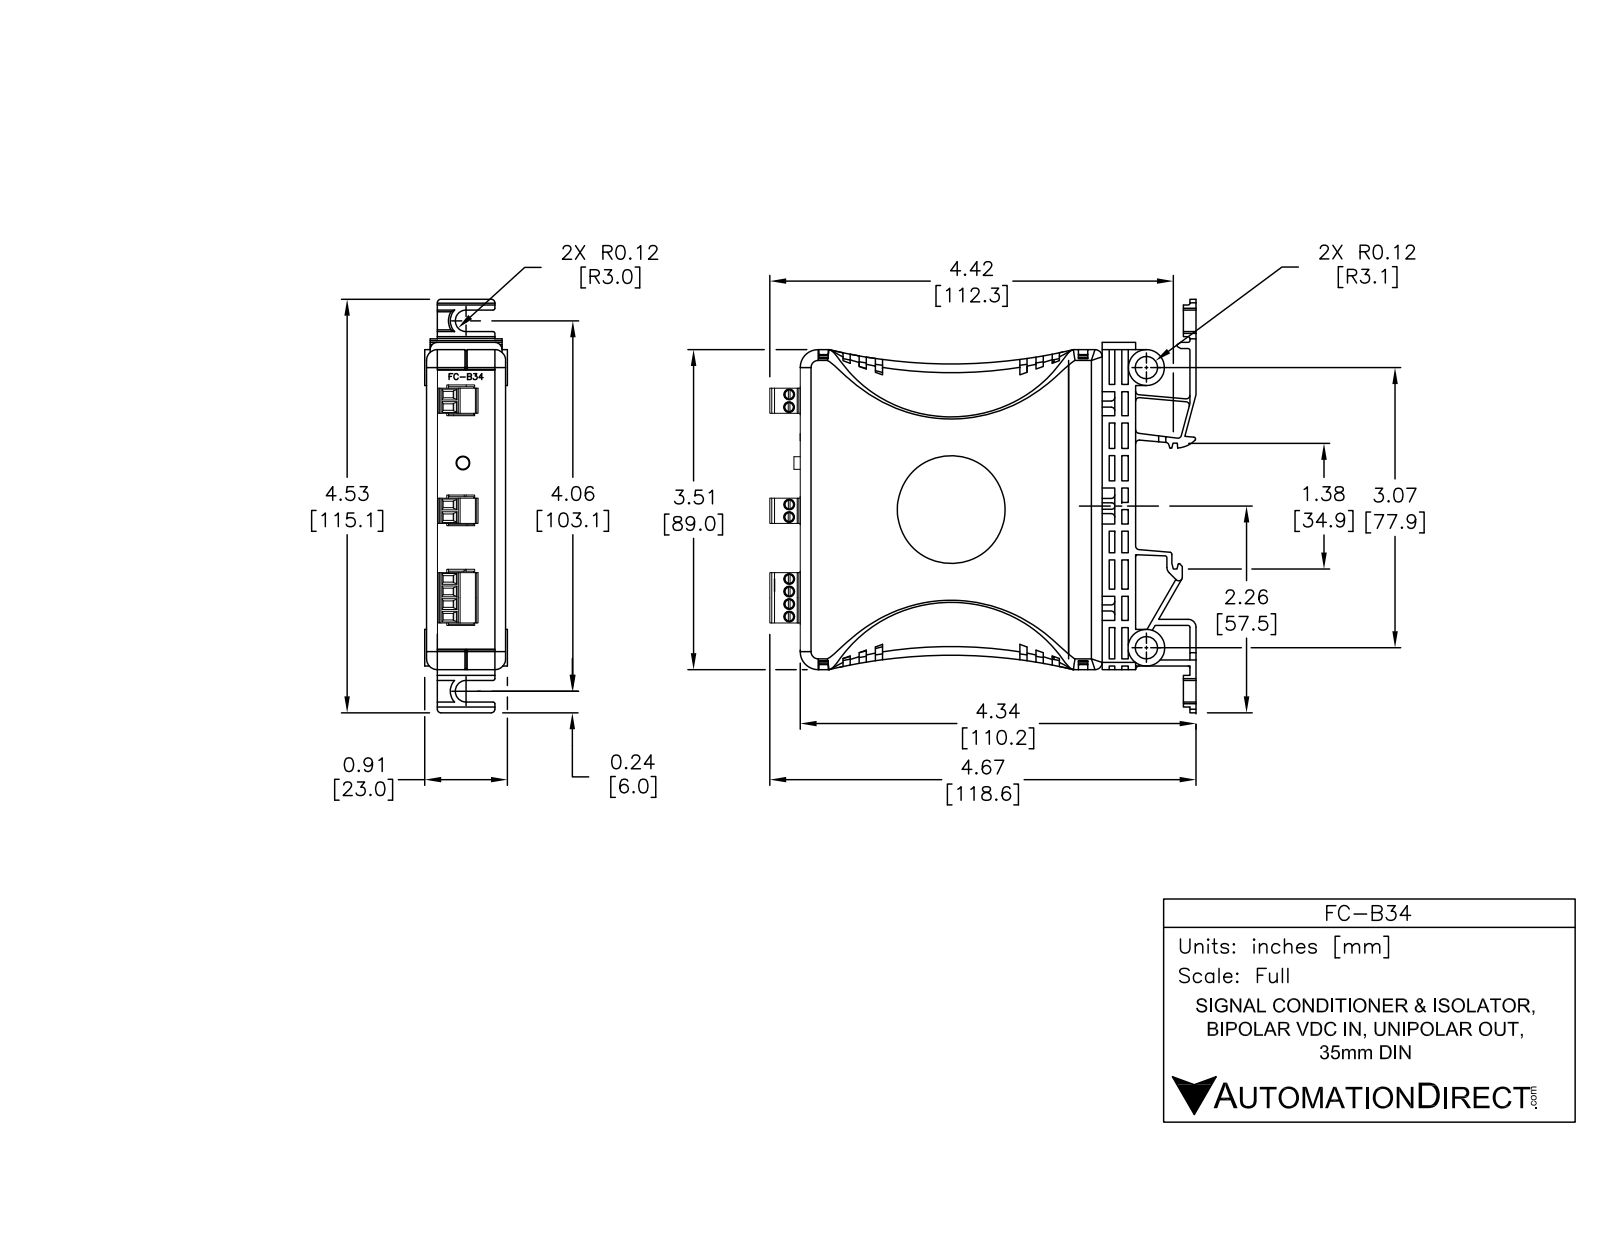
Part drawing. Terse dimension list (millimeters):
name: FC-B34
written by: SolidWorks 2019 (CONFIG_CONTROL_DESIGN)
unit: mm
bodies: 9 solids, 2437 faces (1634 planar, 347 cylindrical, 456 other)
size: 118.94 × 115 × 23
volume: 55 784 mm³; area: 58 305 mm²
holes: 4× ⌀0.4, 2× ⌀6.2
bosses: 1× ⌀13.2, 1× ⌀10.2, 1× ⌀10, 1× ⌀2.3
rounds: 43× R0.5, 36× R1, 27× R0.3, 16× R0.35, 11× R2, 10× R3, 8× R1.4, 7× R0.16
face distances: 1.6, 20.4, 18.8, 22, 1, 0.6, 21, 19.4, 92.8, 92.5
hole spacings: 14, 81, 82.2, 77.9
